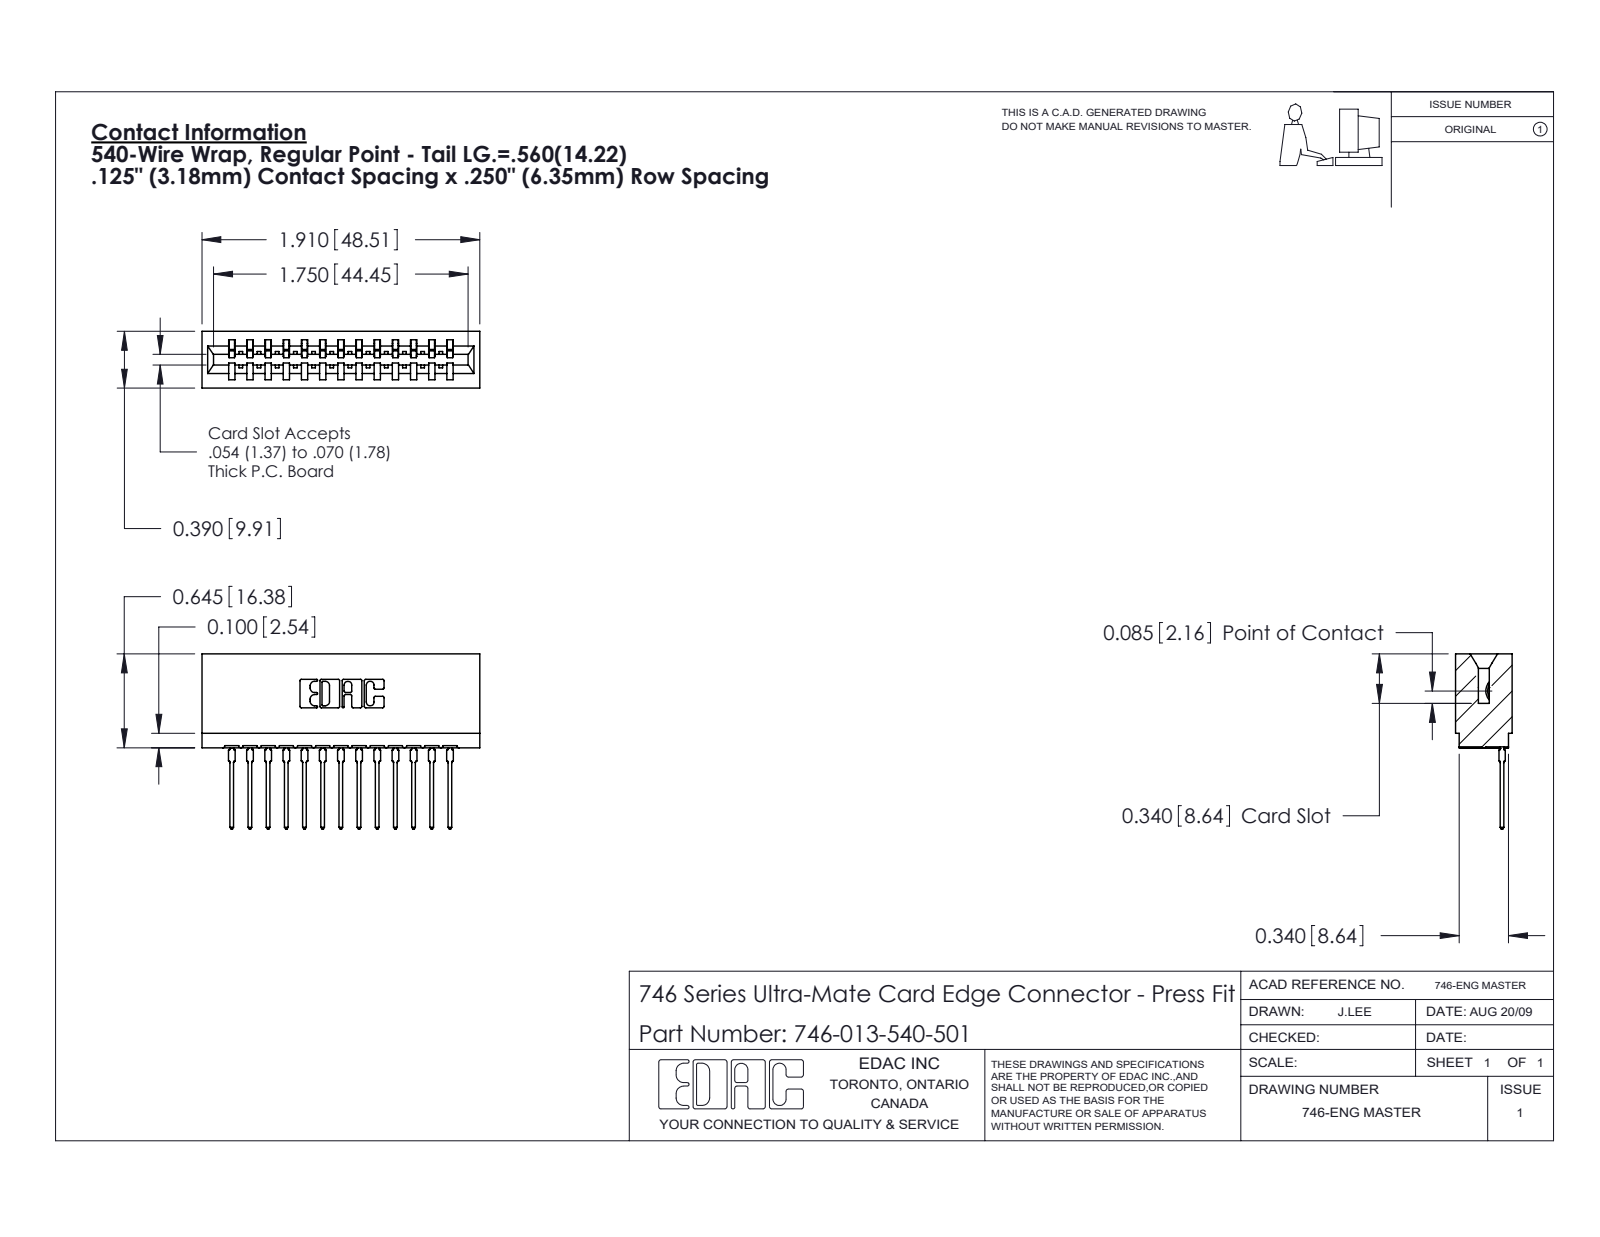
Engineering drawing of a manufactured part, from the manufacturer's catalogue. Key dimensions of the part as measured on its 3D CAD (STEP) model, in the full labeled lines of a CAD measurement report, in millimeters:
Part name (STEP PRODUCT): 746-013-540-501; 746 Part_.340 Slot Depth - 01; 746-292-001_540
STEP written by: SolidWorks 2020 (CONFIG_CONTROL_DESIGN)
Units: millimetres
Bodies: 14 solids, 1501 faces (874 planar, 289 cylindrical, 338 other)
Overall size (bounding box): 48.5 × 30.6 × 9.9
Volume: 5 650 mm³ · Surface area: 7 342 mm²
Partial cylindrical surfaces — rounded edges, fillets, slot ends (radius × count): R0.5 ×26, R0.3 ×22, R0.4 ×14, R0.2 ×6, R0.8 ×6, R0.1 ×4, R0.3 ×4, R0.7 ×3
Main face-to-face distances: 6.4, 8.5, 1.4, 12.7, 3.2, 9.9, 1.1, 7.4, 19.1, 3.2
